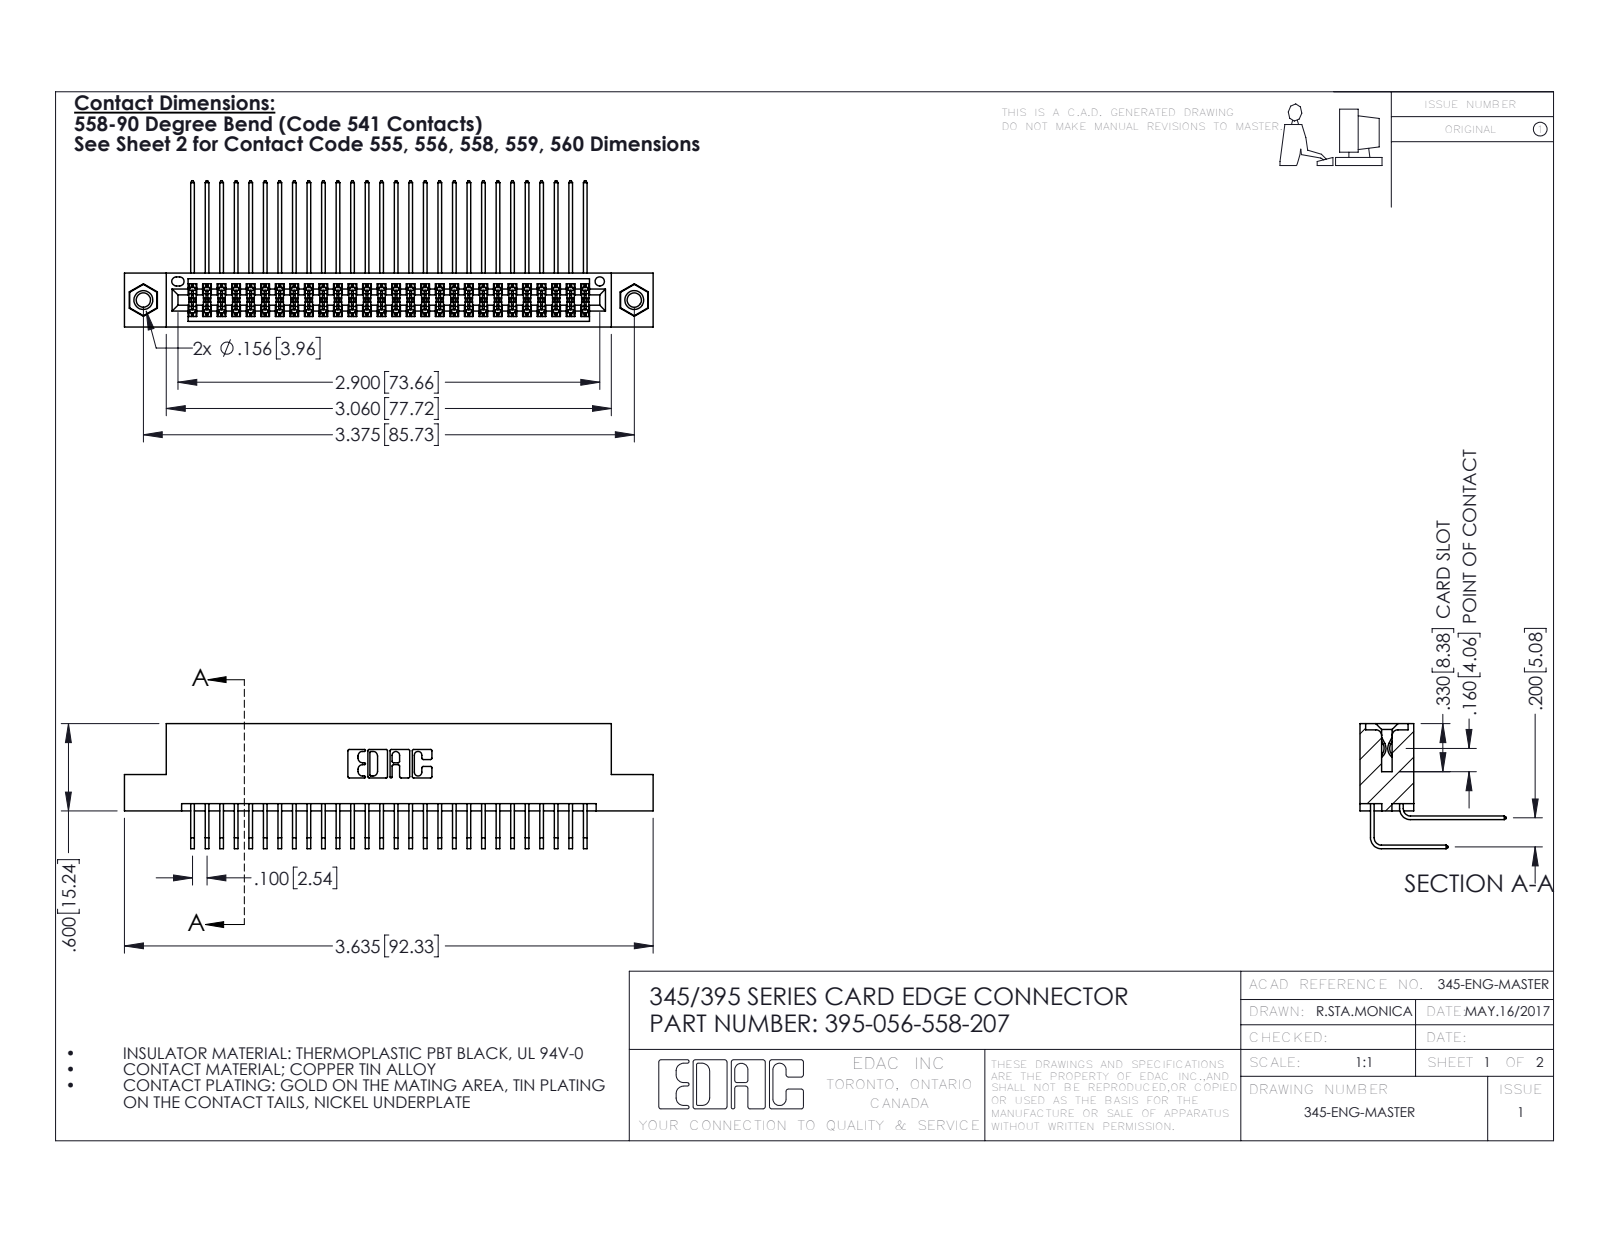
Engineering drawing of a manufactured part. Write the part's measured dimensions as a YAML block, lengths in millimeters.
part_name: "395-056-558-207; 345 Part_Flush Mounting Lugs - 0.156 Dia-TI; 345-250-001_345-250-005-103; 345-292-001_558 Tail - 2 (+1 more)"
step_written_by: "SolidWorks 2016 (CONFIG_CONTROL_DESIGN)"
units: millimeters
bodies: {solids: 59, faces: 3098, planar: 2072, cylindrical: 1010, other: 16}
overall_size: [92.3, 25.5, 21.8]
volume: 9140
surface_area: 14800
round_holes:
  - {diameter: 2.5, count: 2}
  - {diameter: 3.2, count: 2}
  - {diameter: 4, count: 2}
  - {diameter: 1.6, count: 1}
round_bosses_or_shafts:
  - {diameter: 3.9, count: 2}
partial_cylinders:
  - {radius: 0.2, count: 85}
  - {radius: 0.3, count: 22}
  - {radius: 0.2, count: 6}
  - {radius: 0.8, count: 6}
  - {radius: 0.7, count: 3}
  - {radius: 0.4, count: 2}
  - {radius: 0.5, count: 2}
  - {radius: 0.6, count: 2}
face_to_face_distances: [5.1, 1.8, 7.6, 9.4, 2.5, 6.9, 0.6, 5.7, 0.6, 7.2]
hole_center_spacings: [6.9, 79.8, 85.7]
